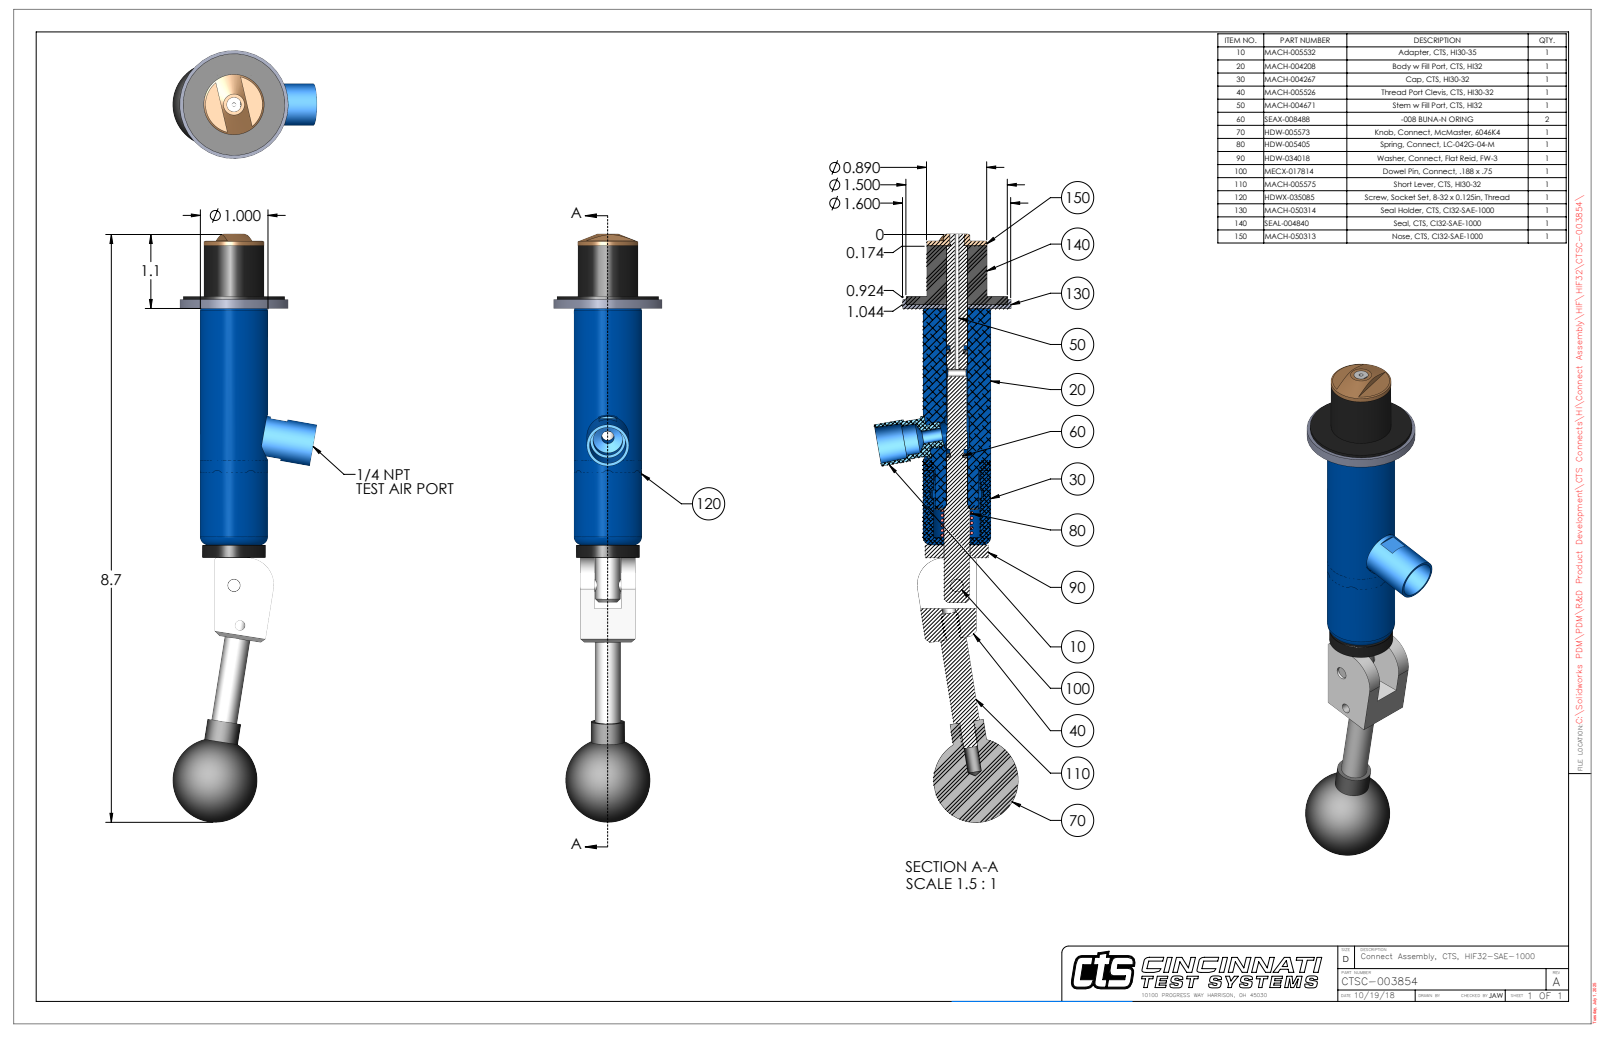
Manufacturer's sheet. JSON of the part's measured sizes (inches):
{"part_name": "CTSC-003854", "step_written_by": "SolidWorks 2023 (AUTOMOTIVE_DESIGN)", "units": "inches", "bodies": {"solids": 9, "faces": 231, "planar": 77, "cylindrical": 96, "other": 58}, "overall_size": [8.692, 2.128, 1.6], "volume_in3": 5.634, "surface_area_in2": 48.08, "round_holes": [[0.201, 2], [0.063, 1], [0.109, 1], [0.15, 1], [0.187, 1], [0.189, 1], [0.213, 1], [0.31, 1], [0.314, 1], [0.316, 1], [0.385, 1], [0.392, 1]], "round_bosses_or_shafts": [[0.25, 2], [0.201, 2], [1.6, 1], [1, 1], [0.936, 1], [0.89, 1], [0.62, 1], [0.5, 1]], "partial_cylinders_radius": [[0.029, 2], [0.068, 1], [0.068, 1], [0.325, 1], [0.4, 1], [0.471, 1]], "face_to_face_distances": [0.06, 0.75, 0.87, 0.93, 0.21, 0.602, 0.12, 0.18, 4.608, 4.42], "hole_center_spacings": [0.599]}
